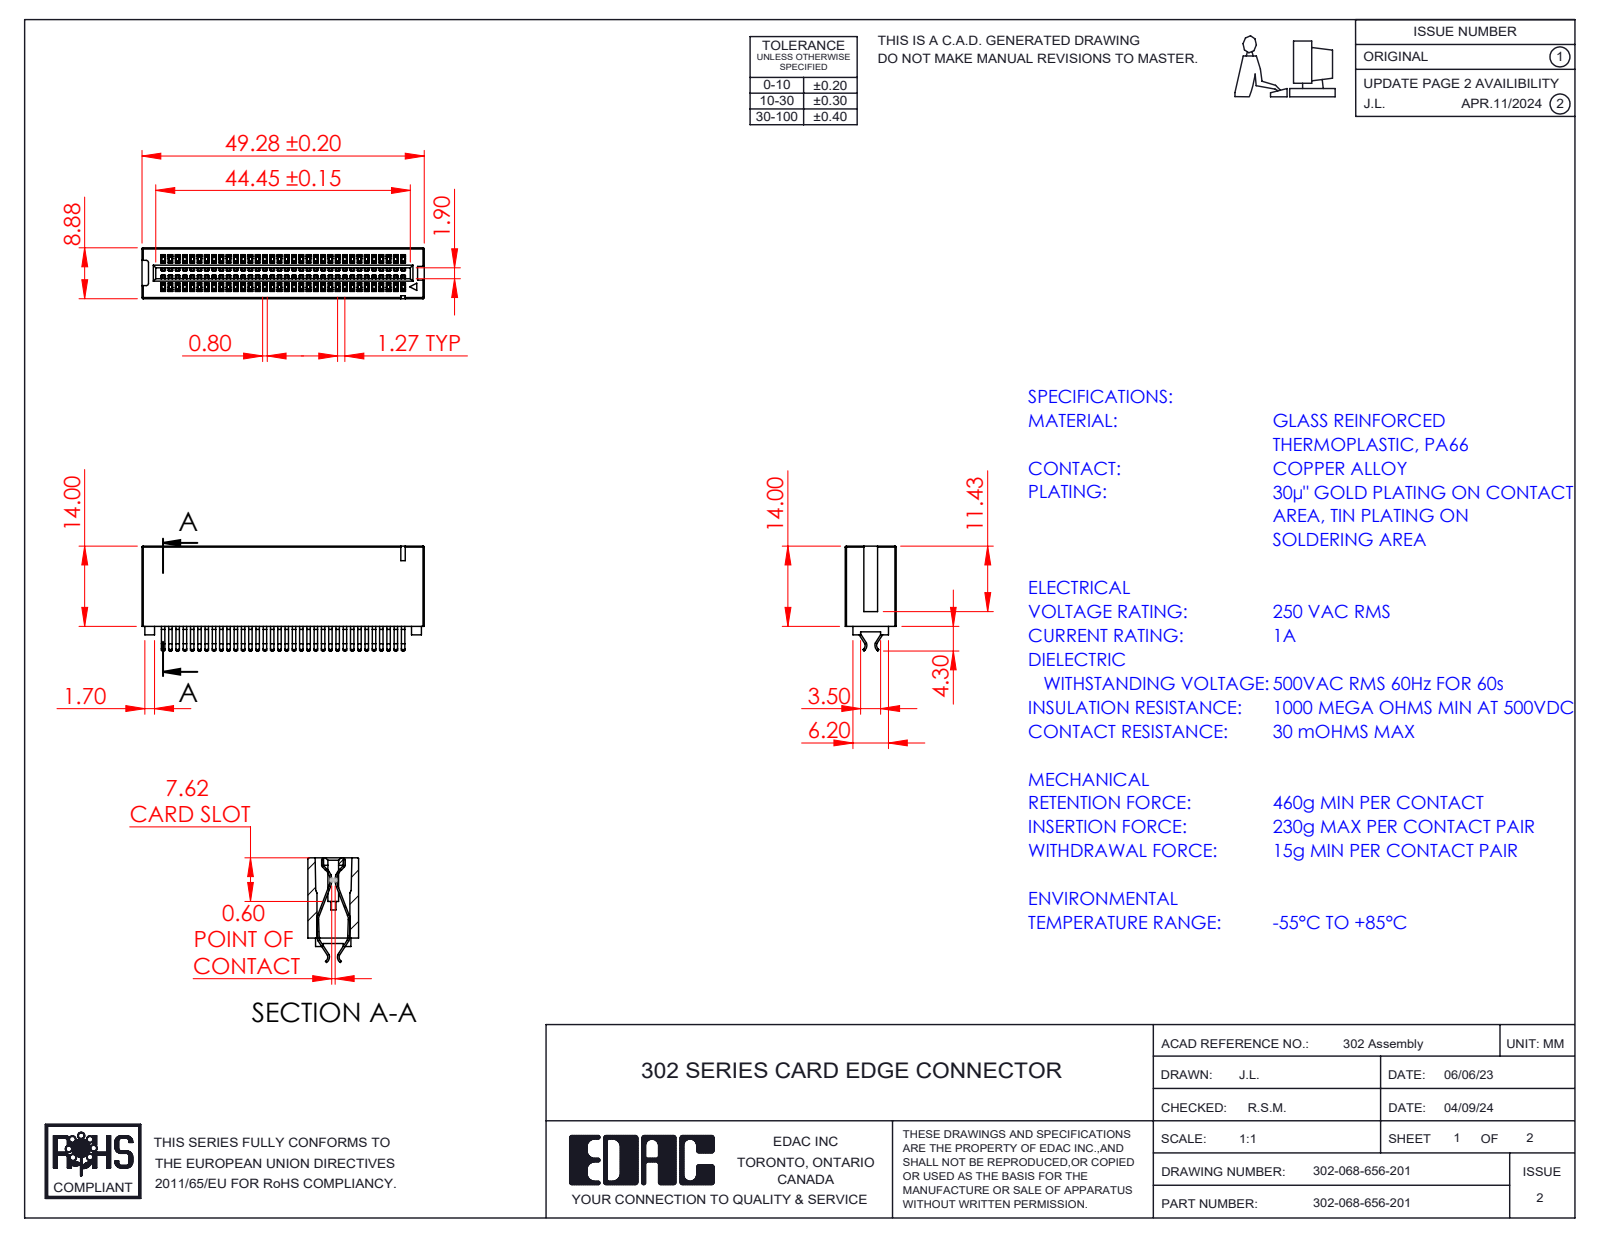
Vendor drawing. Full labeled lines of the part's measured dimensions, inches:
Part name (STEP PRODUCT): HSG_Vertical HSG; 302-068-656-201; Contact_302-290-X56
STEP written by: SolidWorks 2023 (CONFIG_CONTROL_DESIGN)
Units: inches
Bodies: 69 solids, 3296 faces (2191 planar, 1101 cylindrical, 4 other)
Overall size (bounding box): 1.94 × 0.72 × 0.35
Volume: 0.235 in³ · Surface area: 16.37 in²
Partial cylindrical surfaces — rounded edges, fillets, slot ends (radius × count): R0.008 ×212, R0.004 ×2, R0.016 ×2, R0.016 ×2, R0.037 ×2, R0.041 ×2, R0.048 ×2, R0.049 ×2
Main face-to-face distances: 0.05, 0.1, 0.35, 0.15, 0.031, 0.2, 0.019, 0.081, 0.131, 0.25
